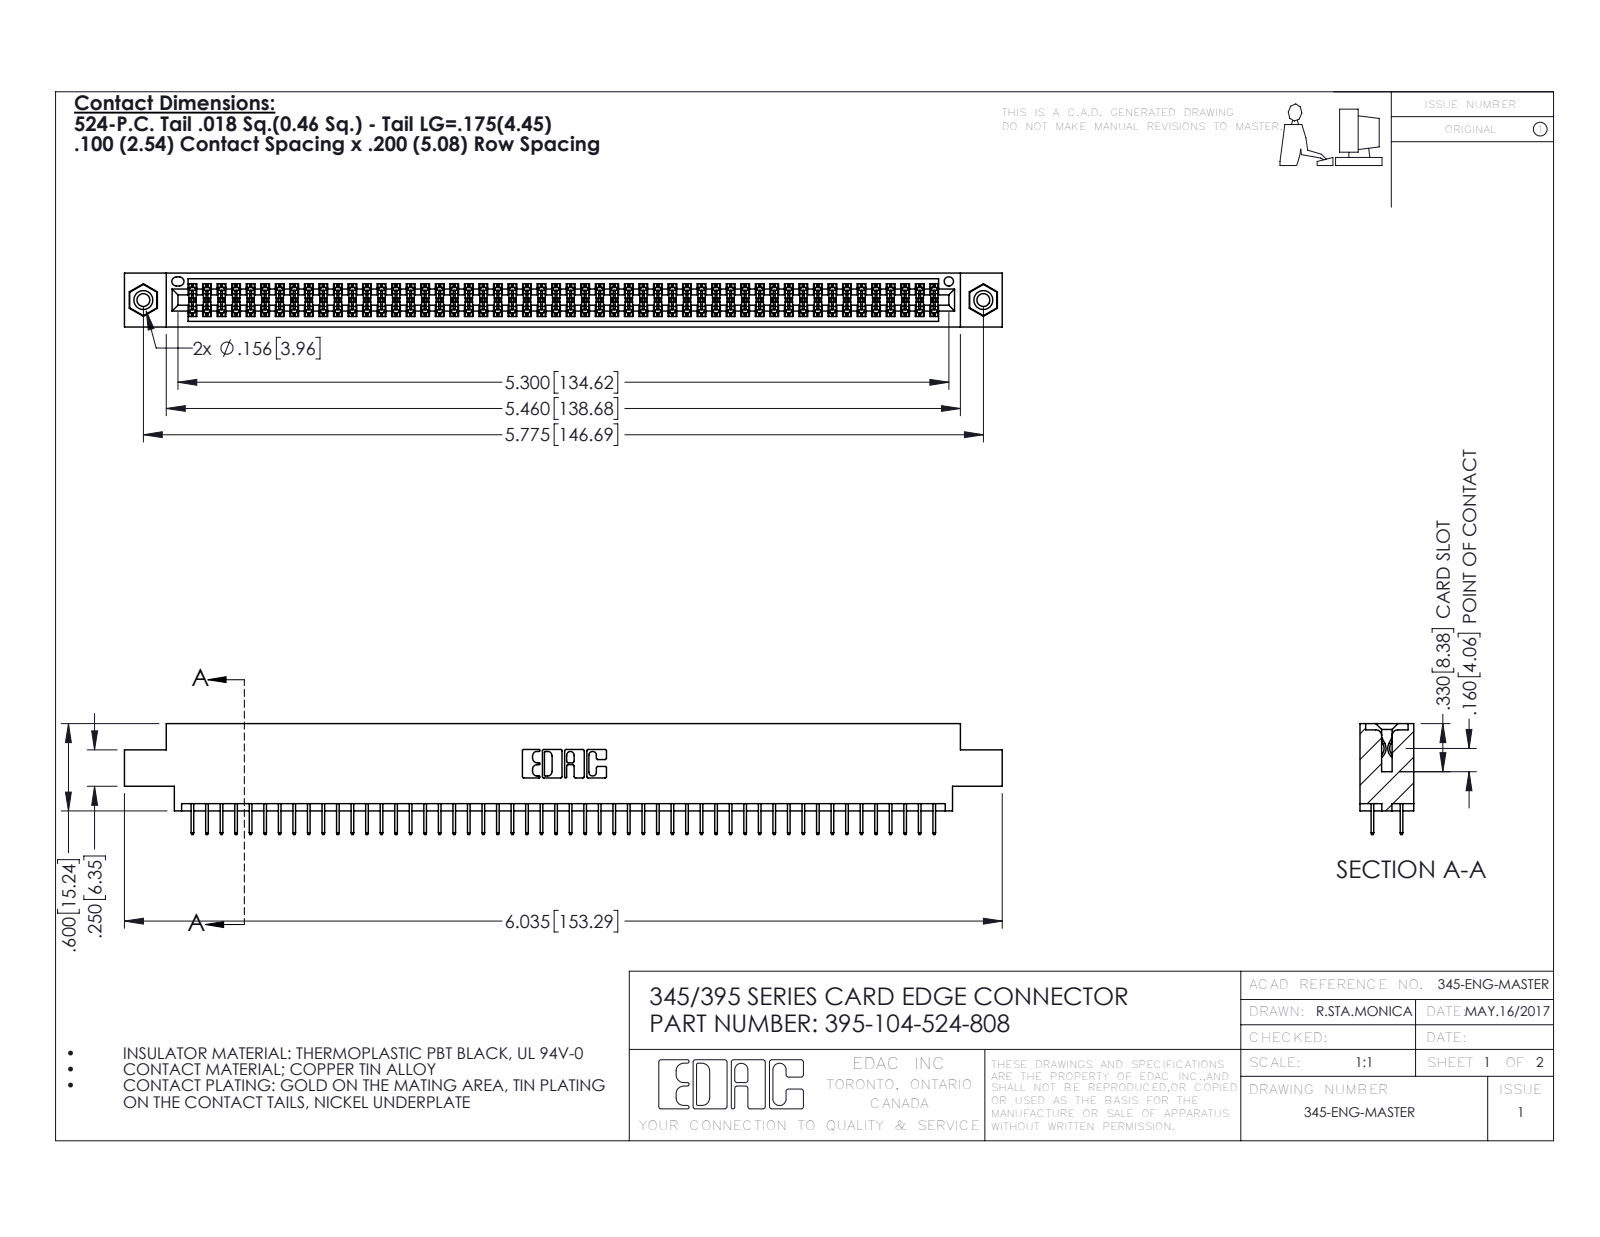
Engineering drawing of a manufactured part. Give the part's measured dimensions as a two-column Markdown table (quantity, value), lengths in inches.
| quantity | value |
| --- | --- |
| part name | 345-250-001_345-250-003-102; 345 Part_0.170 Offset - 0.156 Dia-TI; 345-292-001_345-293-124; 395-104-524-808 |
| STEP written by | SolidWorks 2016 (CONFIG_CONTROL_DESIGN) |
| units | inches |
| bodies | 107 solids, 5806 faces (4172 planar, 1618 cylindrical, 16 other) |
| overall size | 6.035 × 0.762 × 0.37 |
| volume | 0.897 in³ |
| surface area | 33.59 in² |
| round holes (diameter × count) | 0.089 × 2, 0.125 × 2, 0.156 × 2, 0.064 × 1 |
| round bosses / shafts (diameter × count) | 0.155 × 2 |
| partial cylindrical surfaces (radius × count) | 0.006 × 156, 0.01 × 22, 0.007 × 6, 0.031 × 6, 0.026 × 3, 0.014 × 2, 0.019 × 2, 0.022 × 2 |
| main face-to-face distances | 0.072, 0.298, 0.37, 0.2, 0.098, 0.272, 0.025, 0.225, 0.072, 0.175 |
| hole center spacings | 0.27, 5.539, 5.775 |
